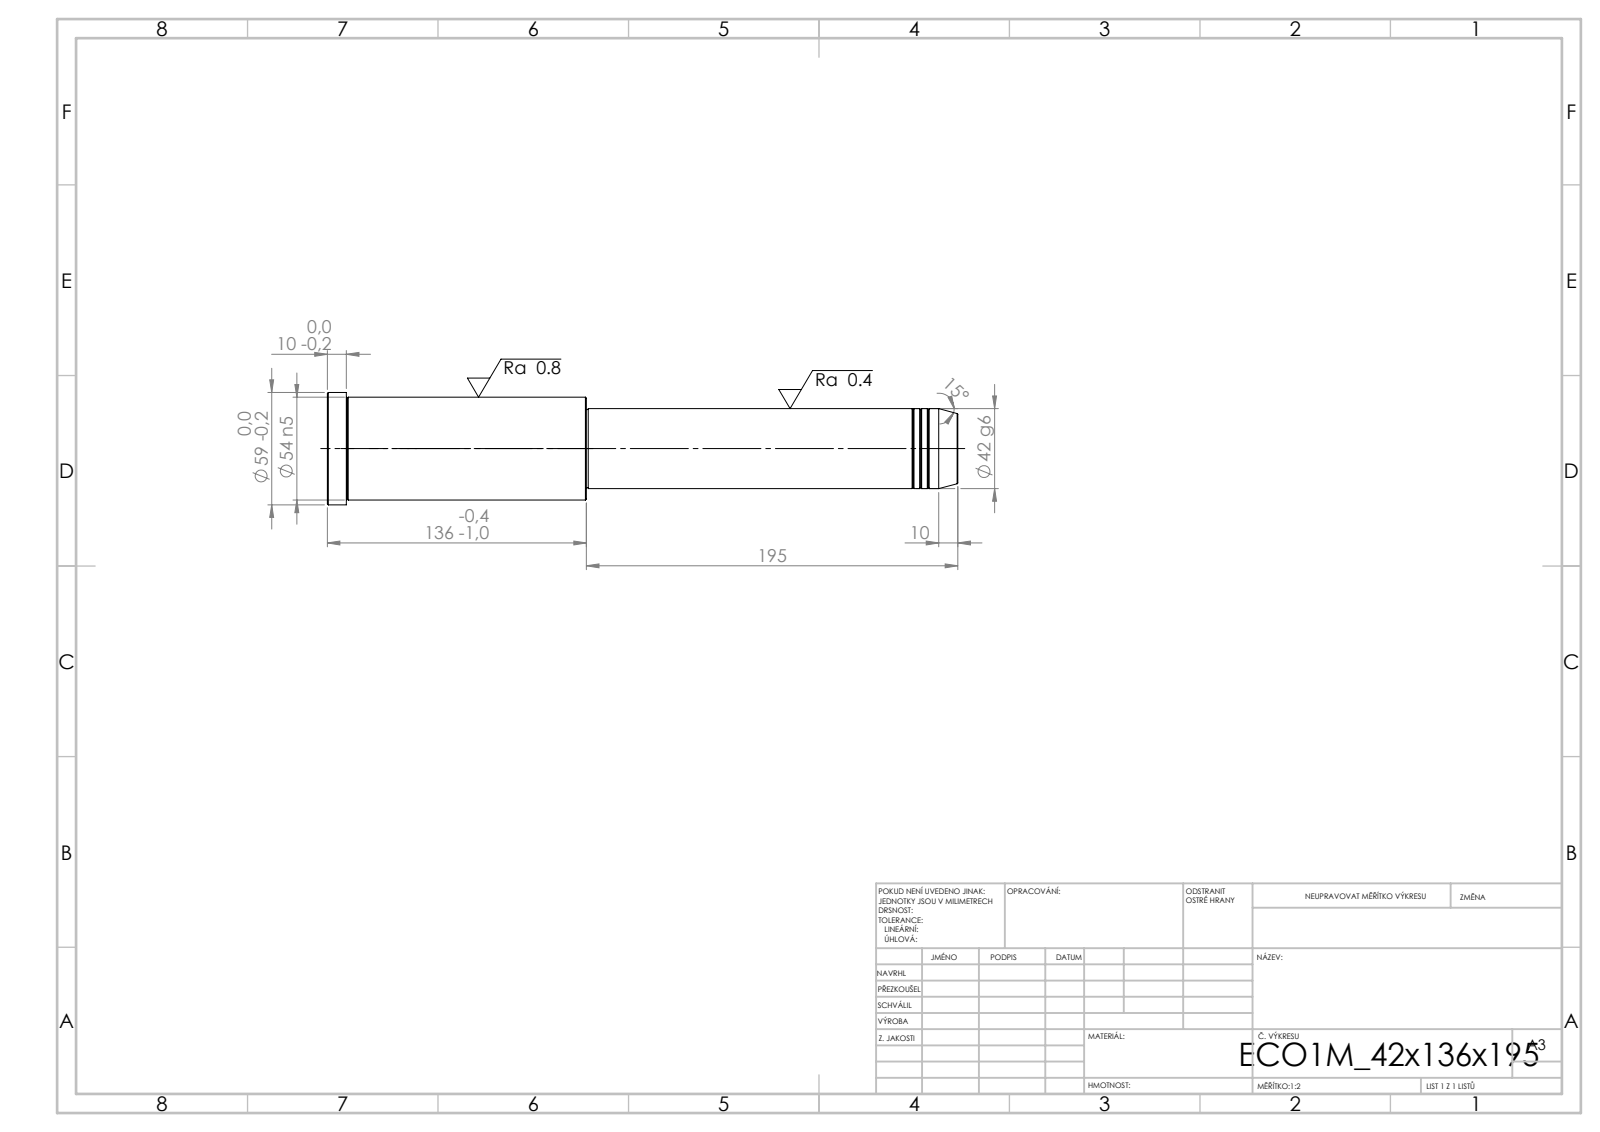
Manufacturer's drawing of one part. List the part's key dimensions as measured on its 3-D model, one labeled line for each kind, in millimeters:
STEP written by: SolidWorks 2019 (CONFIG_CONTROL_DESIGN)
Units: millimetres
Bodies: 1 solid, 43 faces (5 planar, 14 cylindrical, 24 other)
Overall size (bounding box): 331 × 59 × 59
Volume: 584 044 mm³ · Surface area: 54 375 mm²
Round bosses / shafts (diameter × count): ⌀59 ×1, ⌀54 ×1, ⌀42 ×1, ⌀41 ×1
Main face-to-face distances: 331, 195, 136, 321, 126, 10, 194, 1, 127, 137
